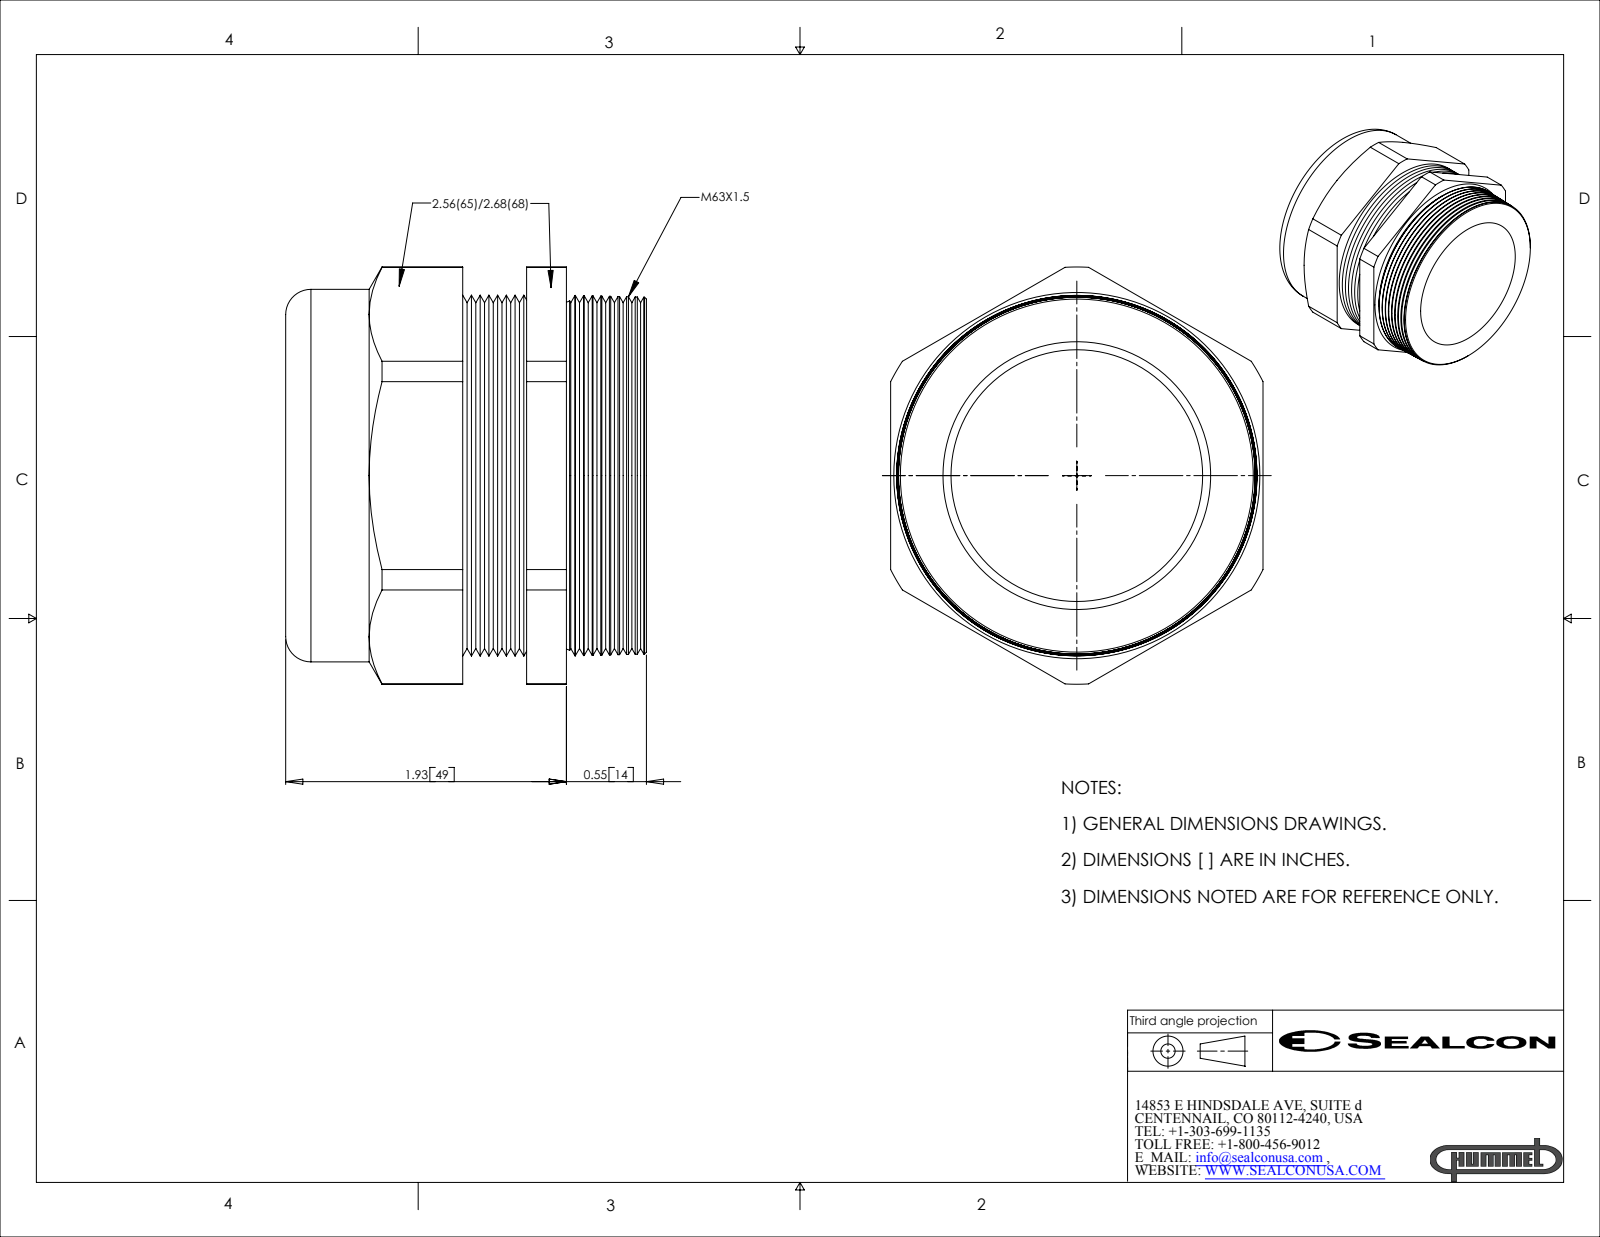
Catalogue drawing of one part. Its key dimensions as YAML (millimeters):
part_name: "CD63MA-GY"
step_written_by: "SolidWorks 2007 (CONFIG_CONTROL_DESIGN)"
units: millimeters
bodies: {solids: 2, faces: 148, planar: 20, cylindrical: 24, other: 104}
overall_size: [72.8, 65, 63]
volume: 107600
surface_area: 37810
round_holes:
  - {diameter: 43.9, count: 1}
  - {diameter: 53.5, count: 1}
  - {diameter: 63, count: 1}
round_bosses_or_shafts:
  - {diameter: 65, count: 1}
partial_cylinders:
  - {radius: 36.4, count: 1}
face_to_face_distances: [65, 48.4, 13.8, 62.2, 41.3, 27.5, 20.9, 30.1, 16.3, 11.2]
